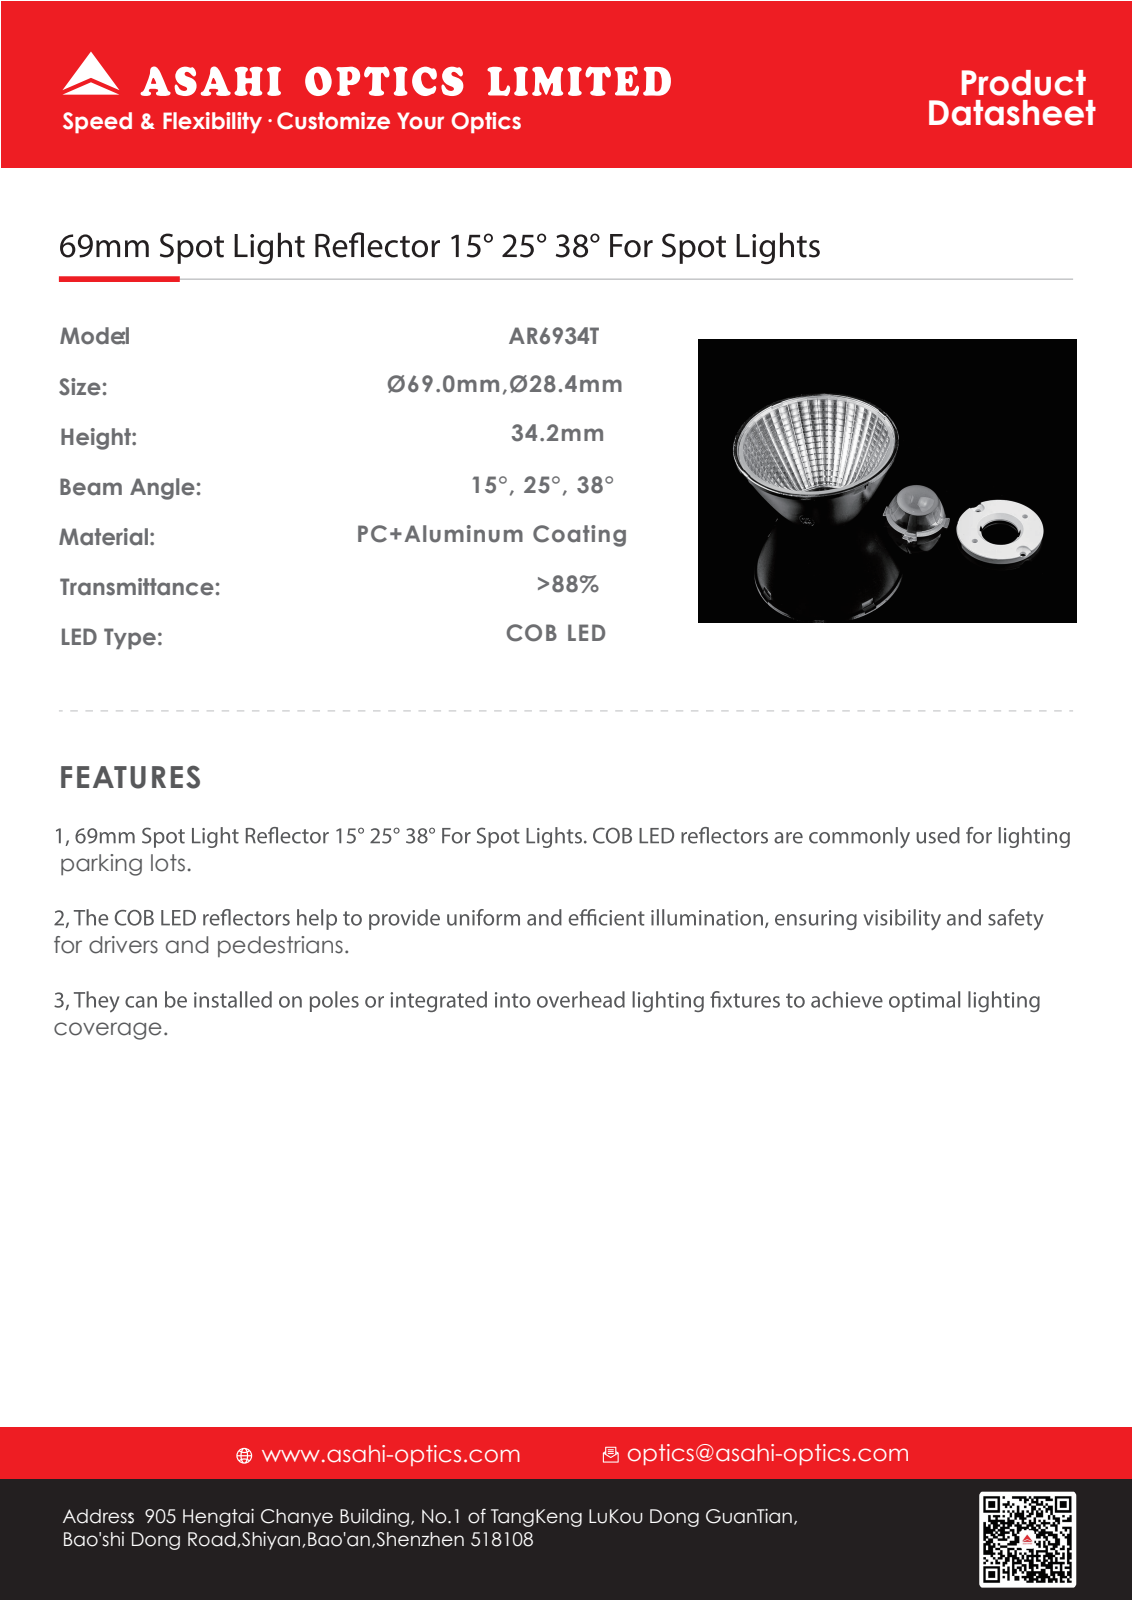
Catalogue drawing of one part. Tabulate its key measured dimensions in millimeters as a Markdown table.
| quantity | value |
| --- | --- |
| part name | SL-A-069C-V3-3D |
| STEP written by | SolidWorks 2014 (CONFIG_CONTROL_DESIGN) |
| units | millimeters |
| bodies | 5 solids, 137 faces (52 planar, 36 cylindrical, 49 other) |
| overall size | 69 × 69 × 36.35 |
| volume | 6 512 mm³ |
| surface area | 13 455 mm² |
| round holes (diameter × count) | 28.4 × 1, 66.2 × 1 |
| round bosses / shafts (diameter × count) | 69 × 1 |
| partial cylindrical surfaces (radius × count) | 0.2 × 12, 15.55 × 1, 16 × 1, 32.75 × 1 |
| main face-to-face distances | 2.9, 0.7, 2.2, 31.3, 32, 34.2, 0.65, 30.65, 31.35, 33.55 |
